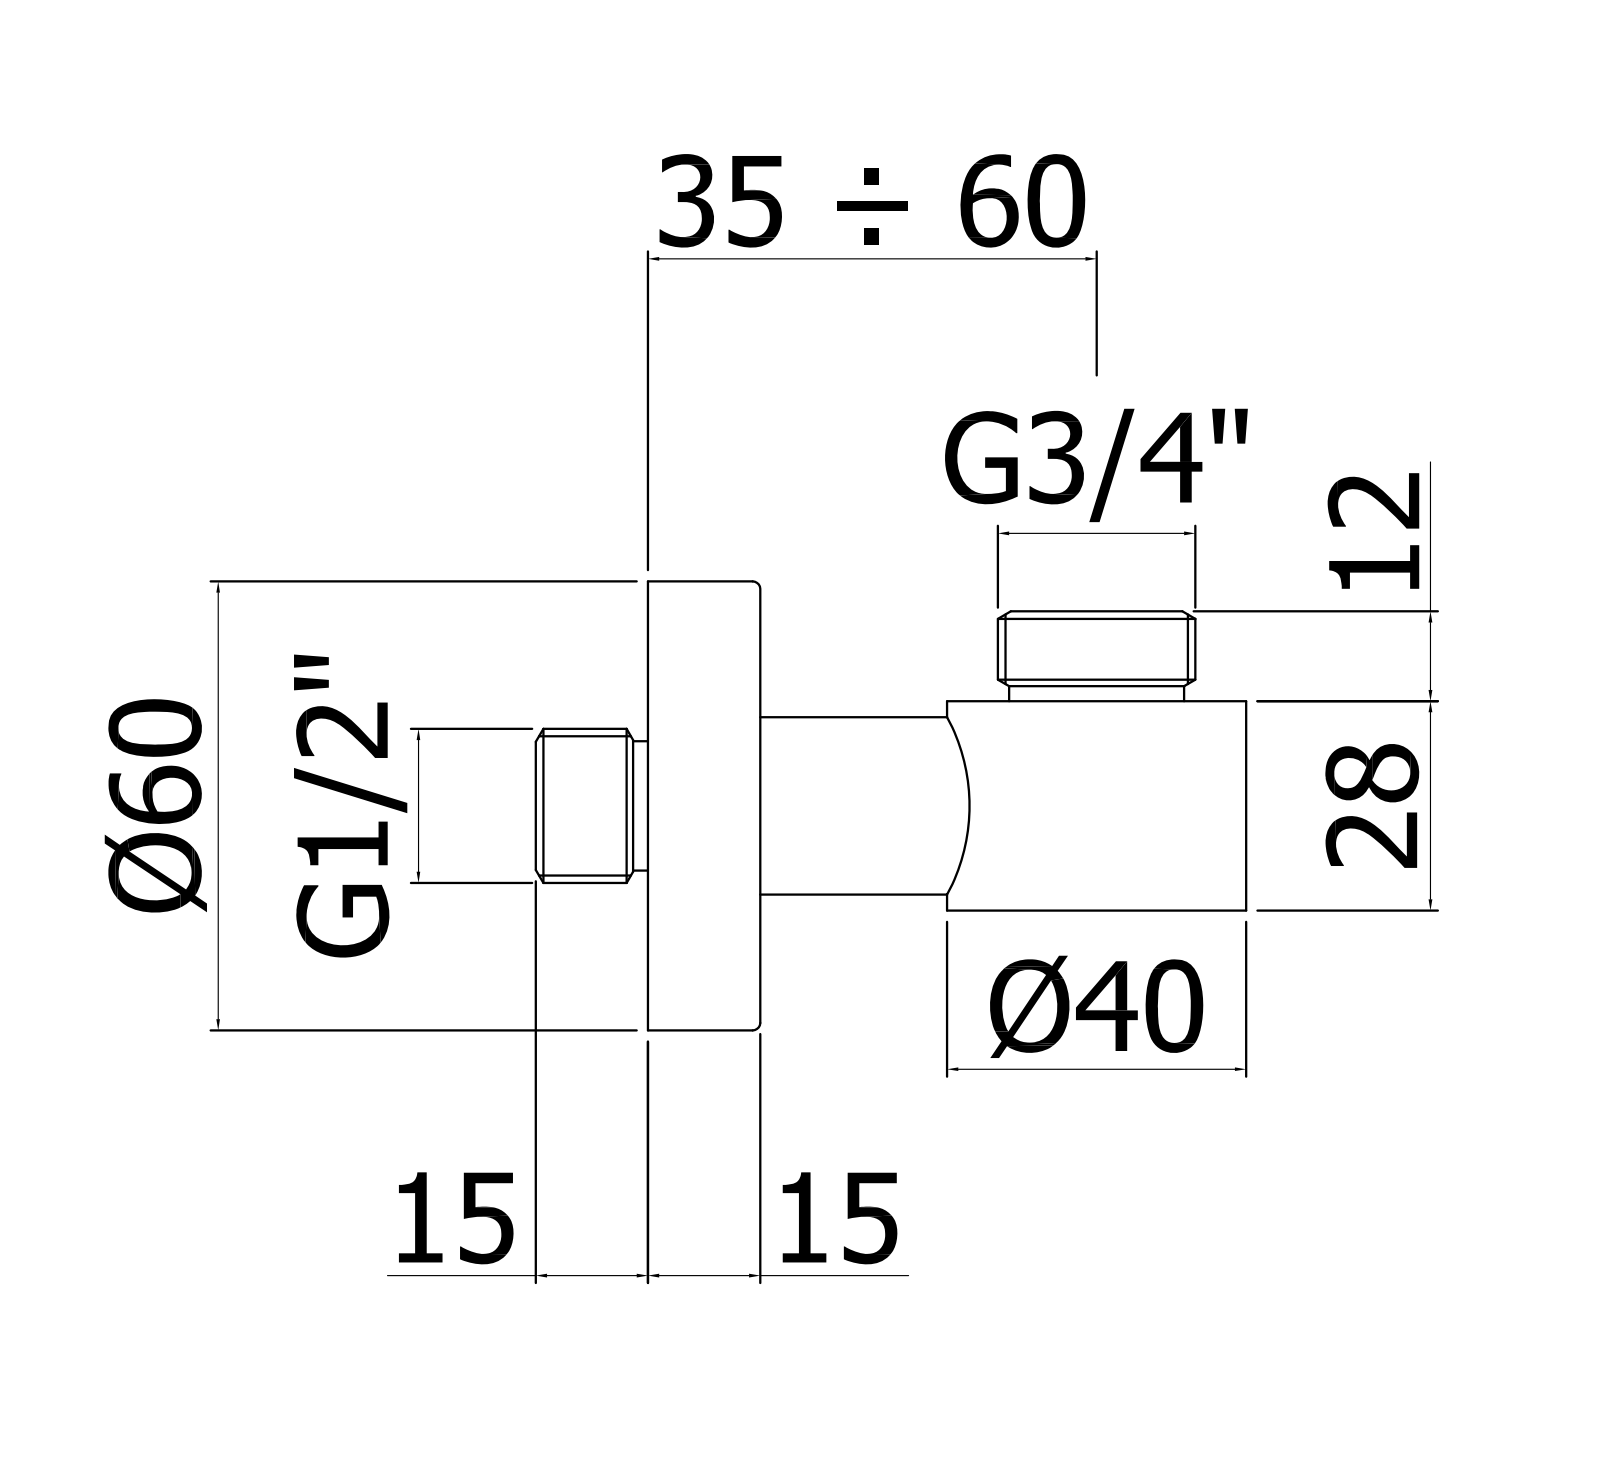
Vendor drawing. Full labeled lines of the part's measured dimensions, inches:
Part name (STEP PRODUCT): ZCOL841CR
STEP written by: CREO PARAMETRIC BY PTC INC, 2020044 (CONFIG_CONTROL_DESIGN)
Units: inches
Bodies: 2 solids, 56 faces (13 planar, 29 cylindrical, 14 other)
Overall size (bounding box): 3.15 × 2.362 × 2.362
Volume: 3.477 in³ · Surface area: 39.07 in²
Round holes (diameter × count): ⌀0.413 ×1, ⌀0.591 ×1, ⌀0.748 ×1, ⌀0.945 ×1, ⌀0.965 ×1, ⌀1.024 ×1, ⌀2.22 ×1
Round bosses / shafts (diameter × count): ⌀2.362 ×1, ⌀1.575 ×1, ⌀1.102 ×1, ⌀1.04 ×1, ⌀0.937 ×1, ⌀0.925 ×1, ⌀0.728 ×1
Partial cylindrical surfaces — rounded edges, fillets, slot ends (radius × count): R0.407 ×1
Main face-to-face distances: 0.098, 1.102, 0.492, 0.591, 1.575, 0.472, 2.165, 1.673, 0.374, 0.118
